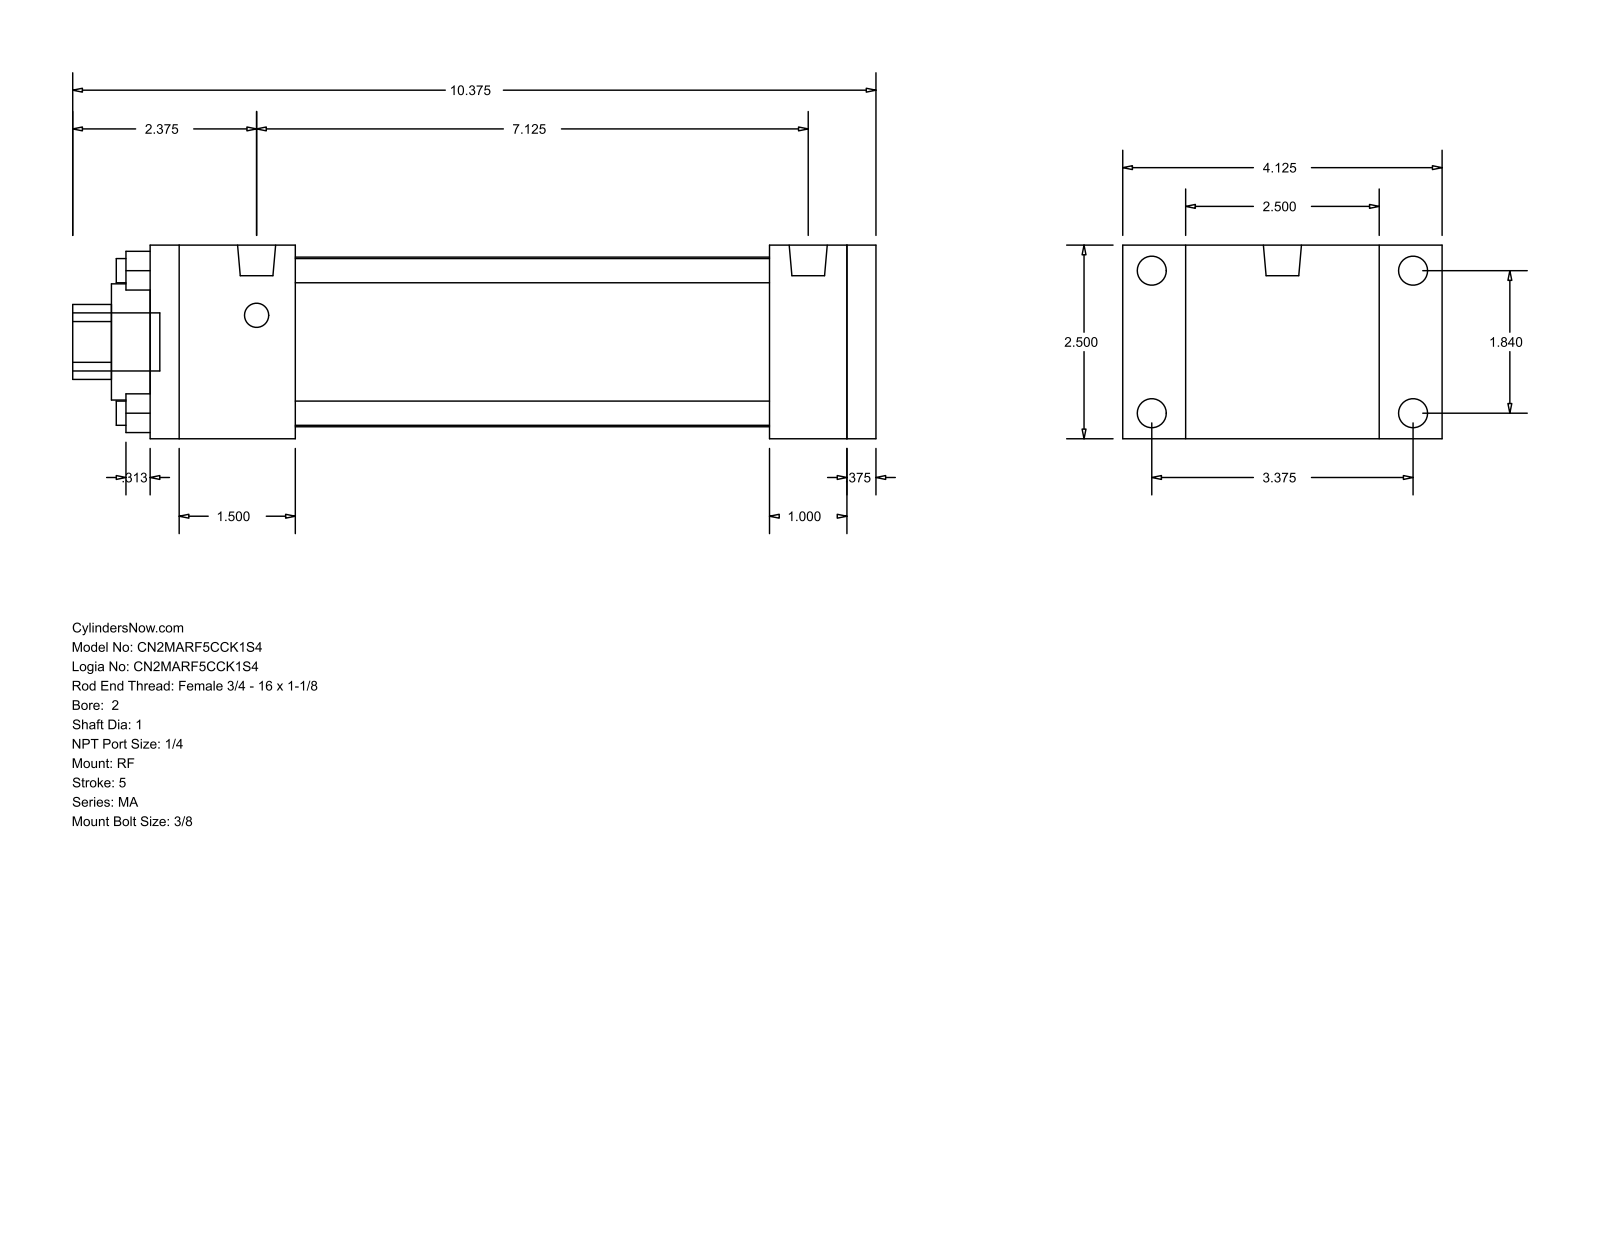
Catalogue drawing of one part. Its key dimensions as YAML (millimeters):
part_name: "MA_RF__0200_1"
step_written_by: "GSSL Pune (CONFIG_CONTROL_DESIGN)"
units: millimeters
bodies: {solids: 0, faces: 92, planar: 64, cylindrical: 28, other: 0}
overall_size: [263.52, 104.78, 63.5]
round_holes:
  - {diameter: 7.94, count: 4}
  - {diameter: 25.4, count: 1}
  - {diameter: 38.1, count: 1}
  - {diameter: 55.63, count: 1}
round_bosses_or_shafts:
  - {diameter: 9.53, count: 4}
  - {diameter: 7.94, count: 4}
  - {diameter: 12.49, count: 2}
  - {diameter: 19.05, count: 1}
partial_cylinders:
  - {radius: 12.29, count: 1}
face_to_face_distances: [63.5, 228.6, 9.52, 238.12, 25.4, 20.64, 12.7, 47.63, 180.97, 190.49]
hole_center_spacings: [33.05, 46.74, 66.1]
